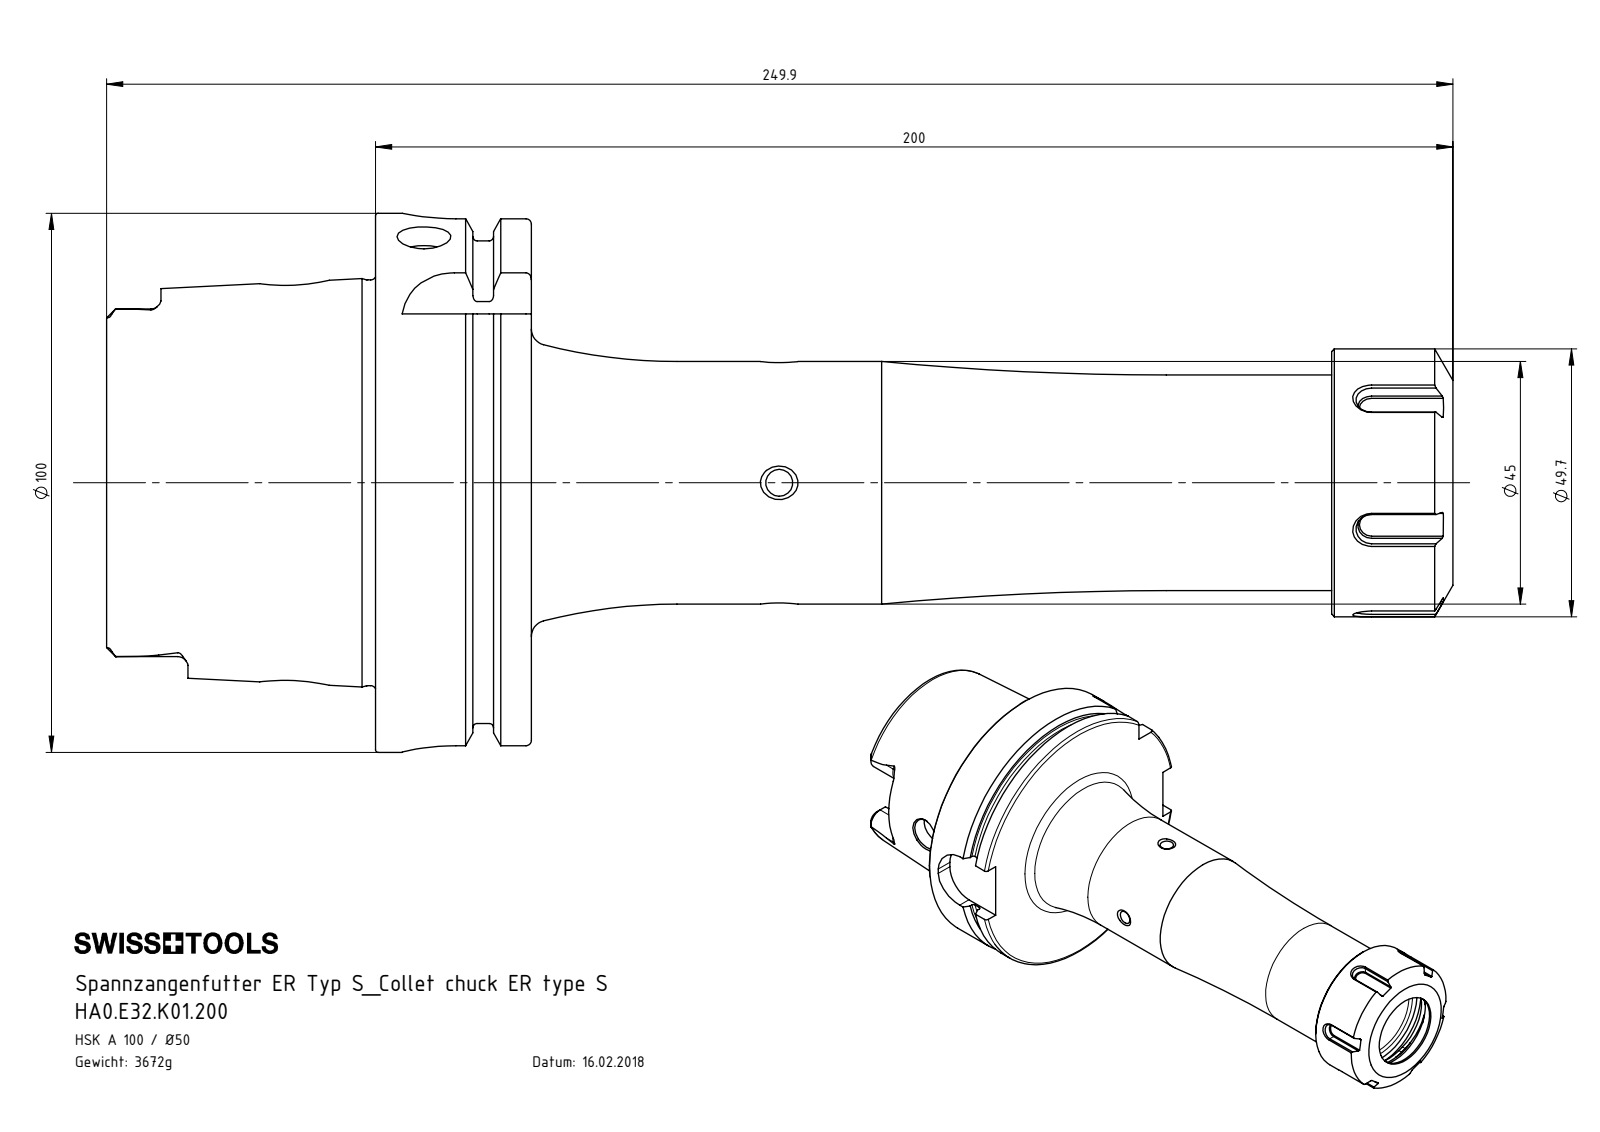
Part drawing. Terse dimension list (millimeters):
name: ERU-AN5.K01.020_A; HA0-E32.K01.200_C_Fertigbearbeitung; HA0.E32.K01.200; E32-ER1.001.022
written by: SolidWorks 2017 (CONFIG_CONTROL_DESIGN)
unit: mm
bodies: 3 solids, 339 faces (126 planar, 81 cylindrical, 132 other)
size: 249.9 × 100 × 100
volume: 467 820 mm³; area: 87 816 mm²
holes: 3× ⌀10, 2× ⌀5, 2× ⌀12, 1× ⌀6, 1× ⌀11, 1× ⌀22.5, 1× ⌀23.5, 1× ⌀26, 1× ⌀27.1, 1× ⌀38.5, 1× ⌀40.5, 1× ⌀53
bosses: 1× ⌀100, 1× ⌀91.95, 1× ⌀75.26, 1× ⌀49.7, 1× ⌀45, 1× ⌀40
rounds: 6× R1.9, 4× R4.88, 4× R10, 2× R15.5
face distances: 28.95, 12.45, 16.5, 49.9, 62.35, 78.85, 227.4, 177.5, 165.05, 148.55
hole spacings: 67.95, 89.95
